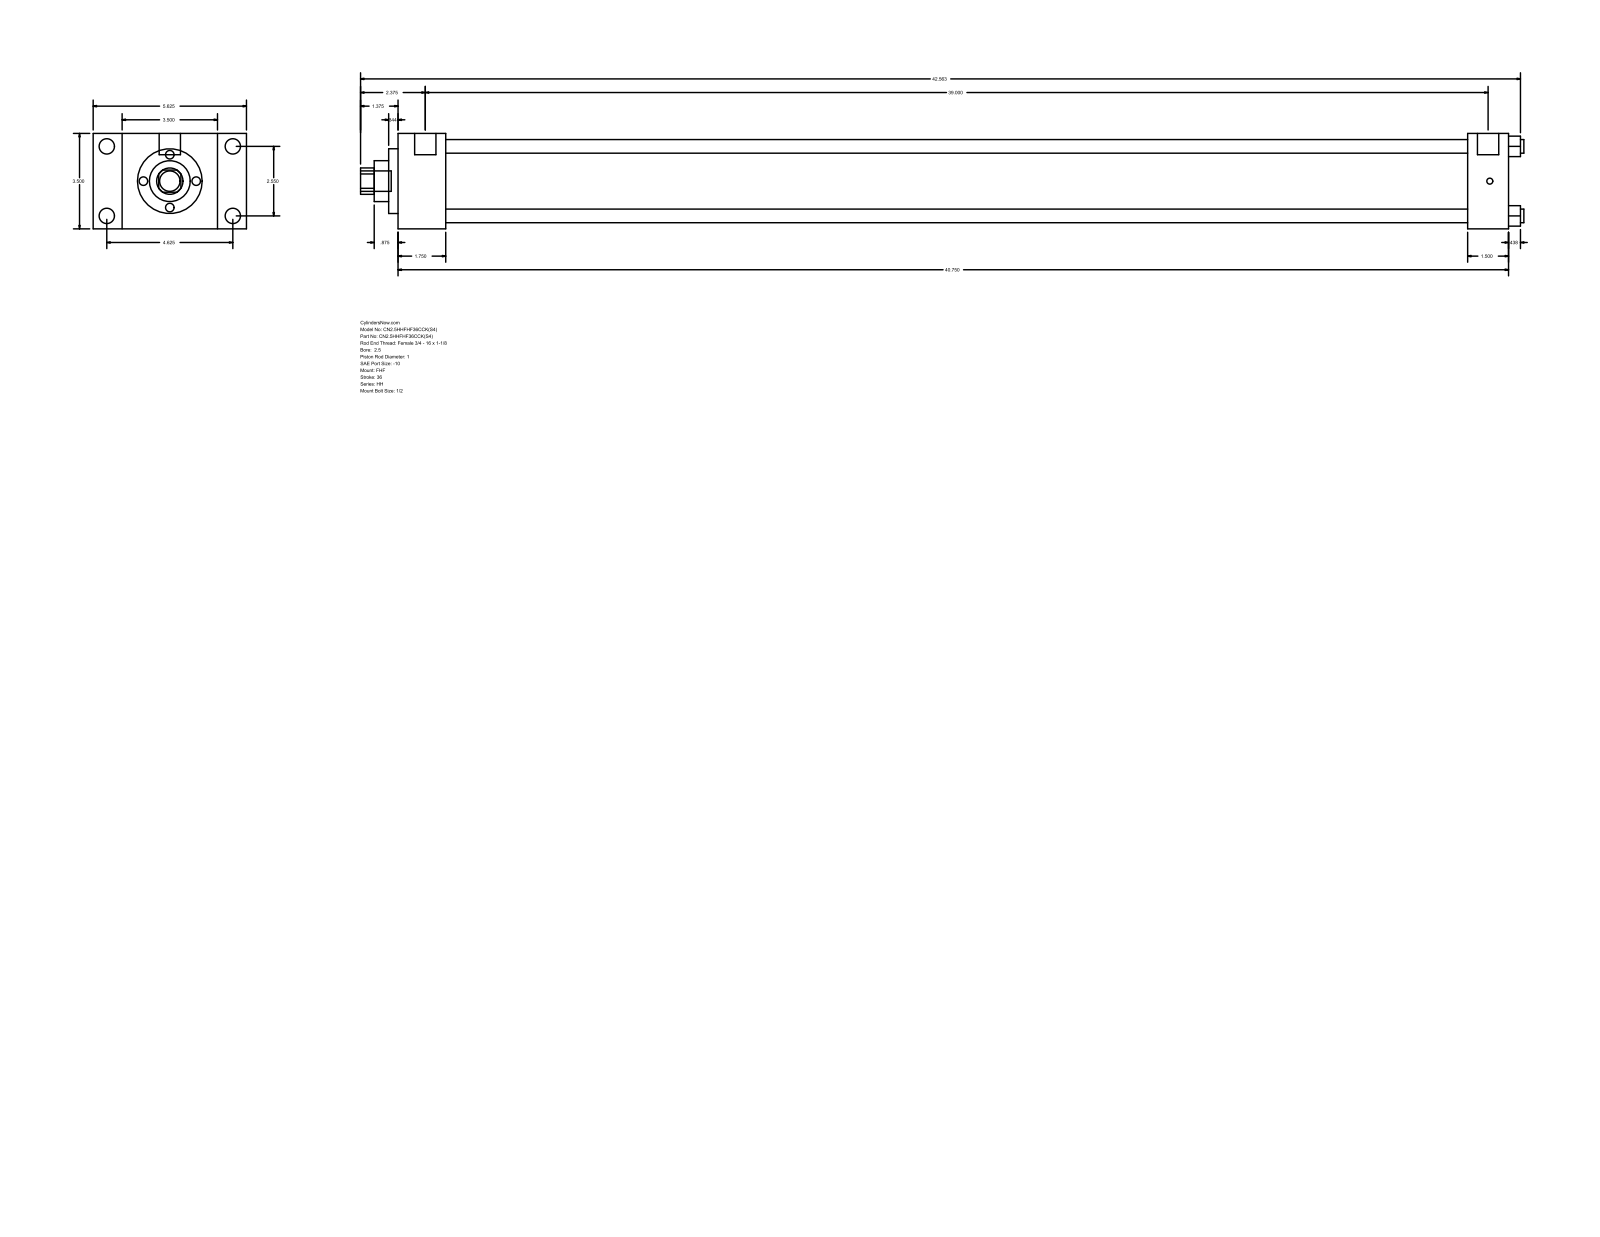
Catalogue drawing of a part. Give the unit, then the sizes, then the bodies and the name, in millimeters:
Units: millimetres
Overall size (bounding box): 1084.26 × 142.88 × 88.9
Round holes (diameter × count): ⌀12.7 ×4, ⌀25.4 ×1, ⌀38.1 ×1, ⌀60.33 ×1, ⌀73.03 ×1
Round bosses / shafts (diameter × count): ⌀14.3 ×4, ⌀5.56 ×4, ⌀19.84 ×2, ⌀19.05 ×1
Partial cylindrical surfaces — rounded edges, fillets, slot ends (radius × count): R12.29 ×1
Main face-to-face distances: 88.9, 44.46, 26.99, 115.89, 1035.05, 990.59, 142.88, 996.96, 952.5, 38.09
Hole centre spacings: 45.79, 64.76, 91.58
Bodies: 0 solids, 90 faces (61 planar, 29 cylindrical, 0 other)
Part name (STEP PRODUCT): HH_FHF__0250_1
STEP written by: GSSL Pune (CONFIG_CONTROL_DESIGN)
